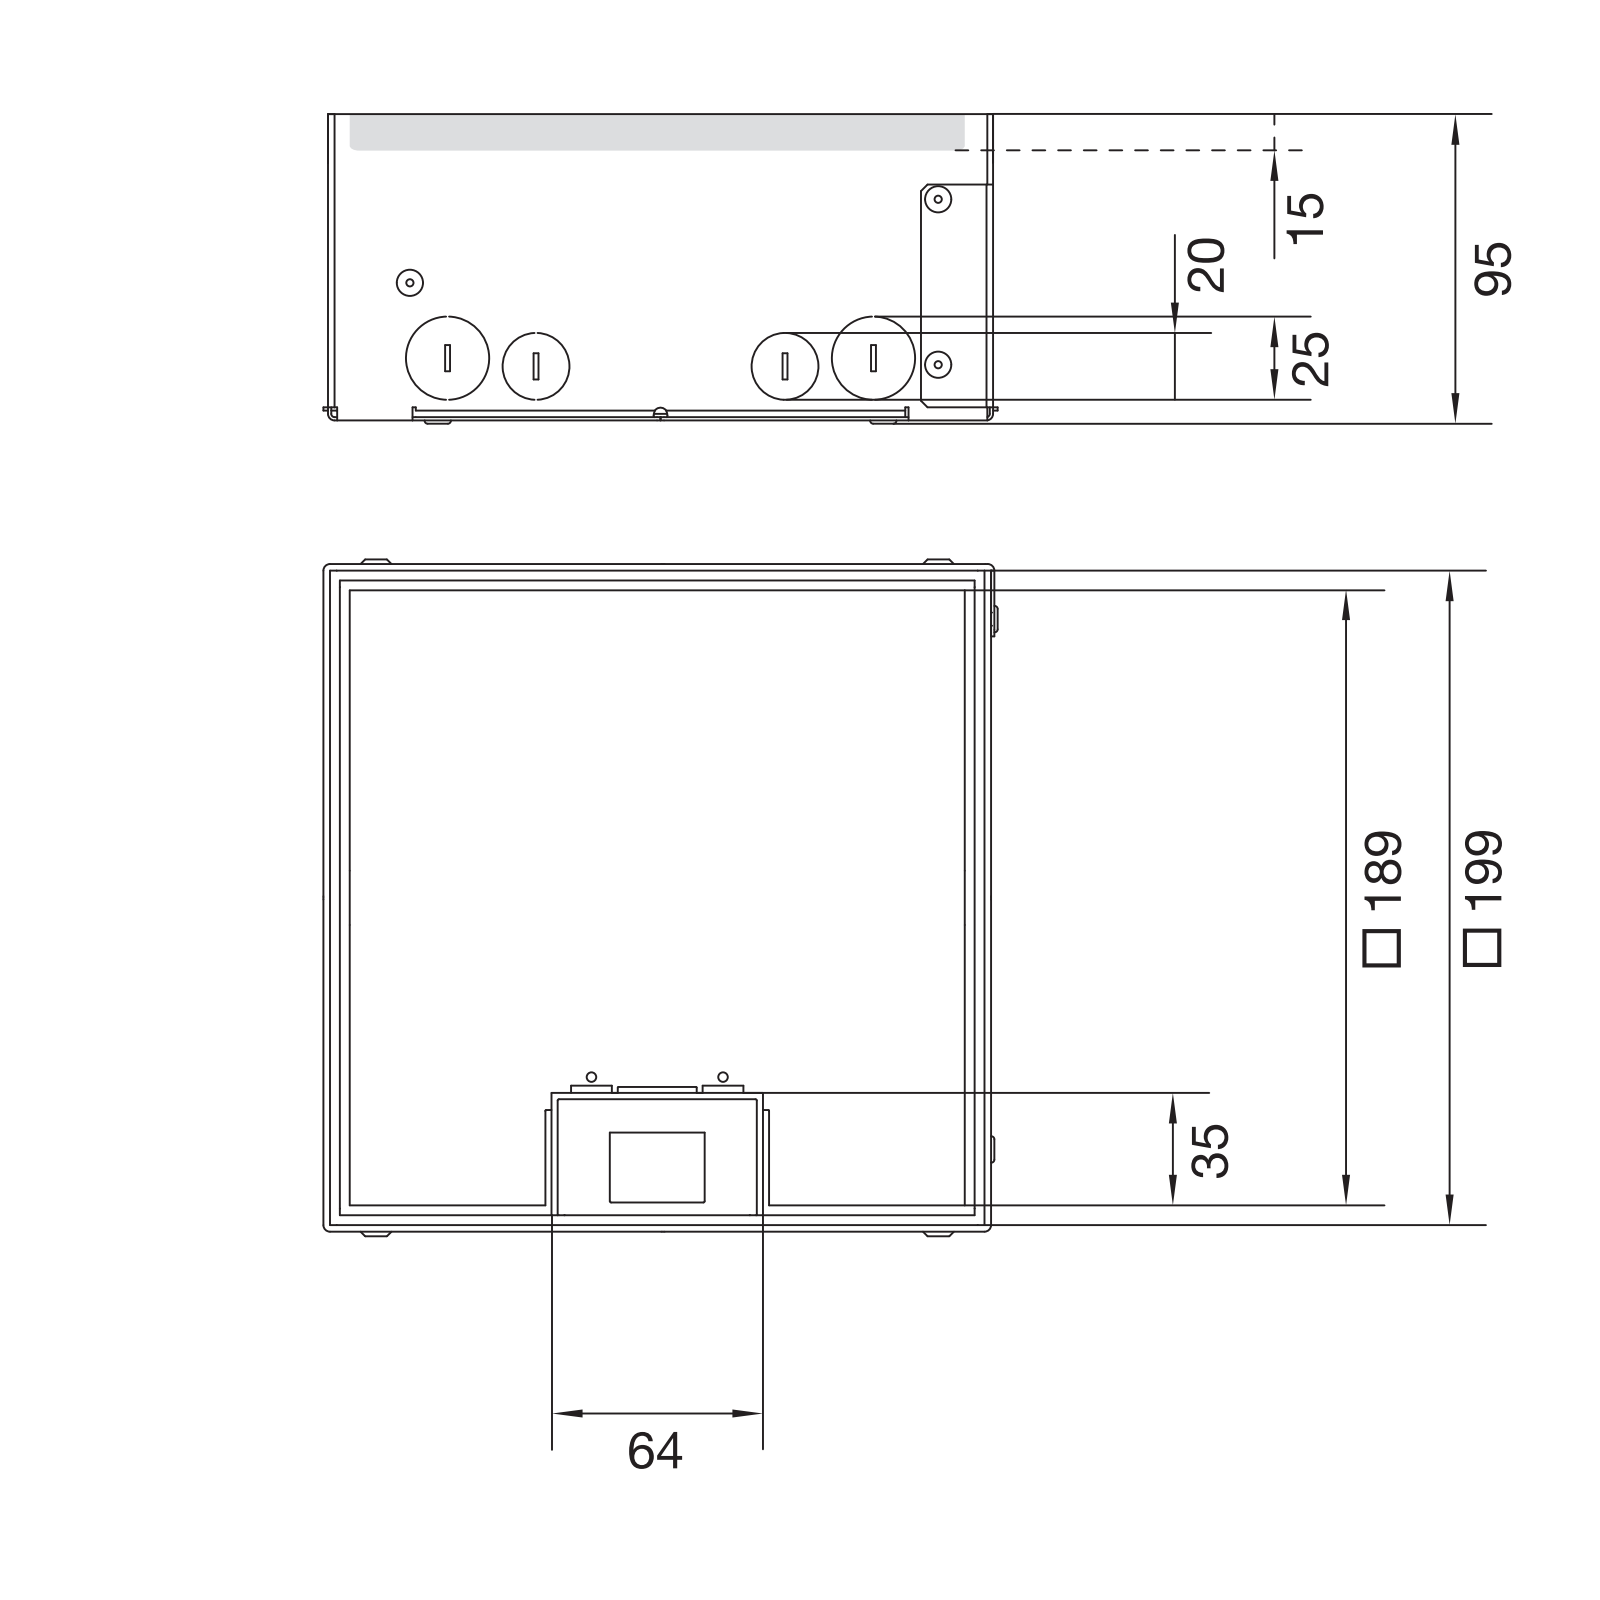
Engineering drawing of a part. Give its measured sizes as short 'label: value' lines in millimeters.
name: T-00657; 60449-M; 60450-M; T-00714 (+8 more)
written by: CREO PARAMETRIC BY PTC INC, 2022024 (AUTOMOTIVE_DESIGN)
unit: mm
bodies: 28 solids, 1521 faces (950 planar, 337 cylindrical, 234 other)
size: 203.25 × 203 × 93.5
volume: 421 669 mm³; area: 569 123 mm²
holes: 12× ⌀20.4, 8× ⌀25.4, 4× ⌀6.8, 4× ⌀7.5, 4× ⌀18.5, 2× ⌀2.7
bosses: 16× ⌀20, 8× ⌀25, 4× ⌀20.5, 4× ⌀12, 4× ⌀11.5, 4× ⌀9.85, 4× ⌀8.5, 4× ⌀8
rounds: 21× R1, 16× R5, 12× R3, 8× R2.1, 7× R2, 6× R2.25, 5× R105, 1× R6.6
face distances: 1, 2, 202, 201, 3, 5, 76.5, 203, 75.5, 77.5
hole spacings: 27.12, 71.94, 103.03, 171, 27.23, 41.72, 42.43, 43.14
